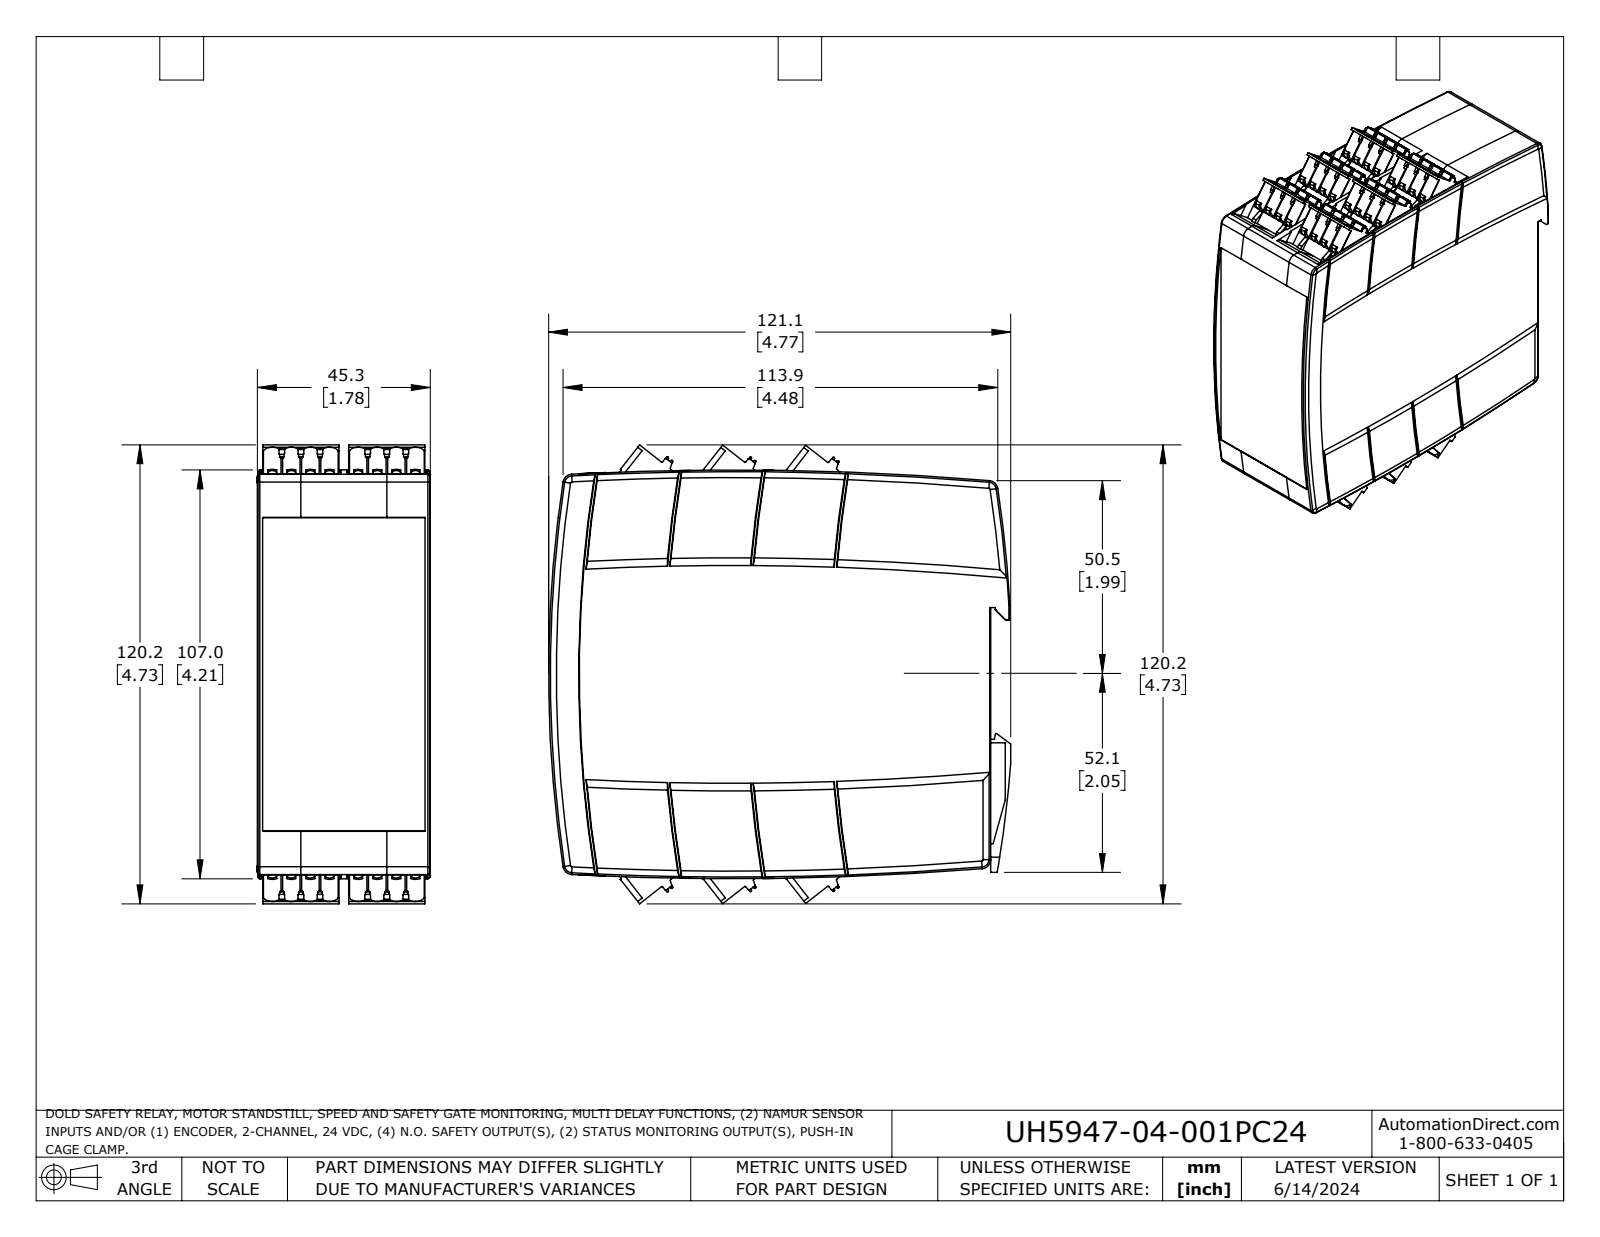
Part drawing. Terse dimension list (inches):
name: PC_UH5947
written by: SolidWorks 2023 (AUTOMOTIVE_DESIGN)
unit: in
bodies: 1 solid, 6750 faces (4956 planar, 1557 cylindrical, 237 other)
size: 4.766 × 4.731 × 1.783
volume: 33.21 in³; area: 106 in²
holes: 48× ⌀0.157, 6× ⌀0.029
bosses: 6× ⌀0.032
rounds: 96× R0.046, 48× R0.059, 48× R0.098, 48× R0.112, 24× R0.012, 18× R0.008, 18× R0.013, 18× R0.013
face distances: 1.776, 1.768, 1.783, 0.886, 0.806, 0.02, 4.455, 0.021, 0.806, 0.785
hole spacings: 0.704, 0.197, 0.394, 0.886, 1.276, 1.365, 0.689, 1.083
